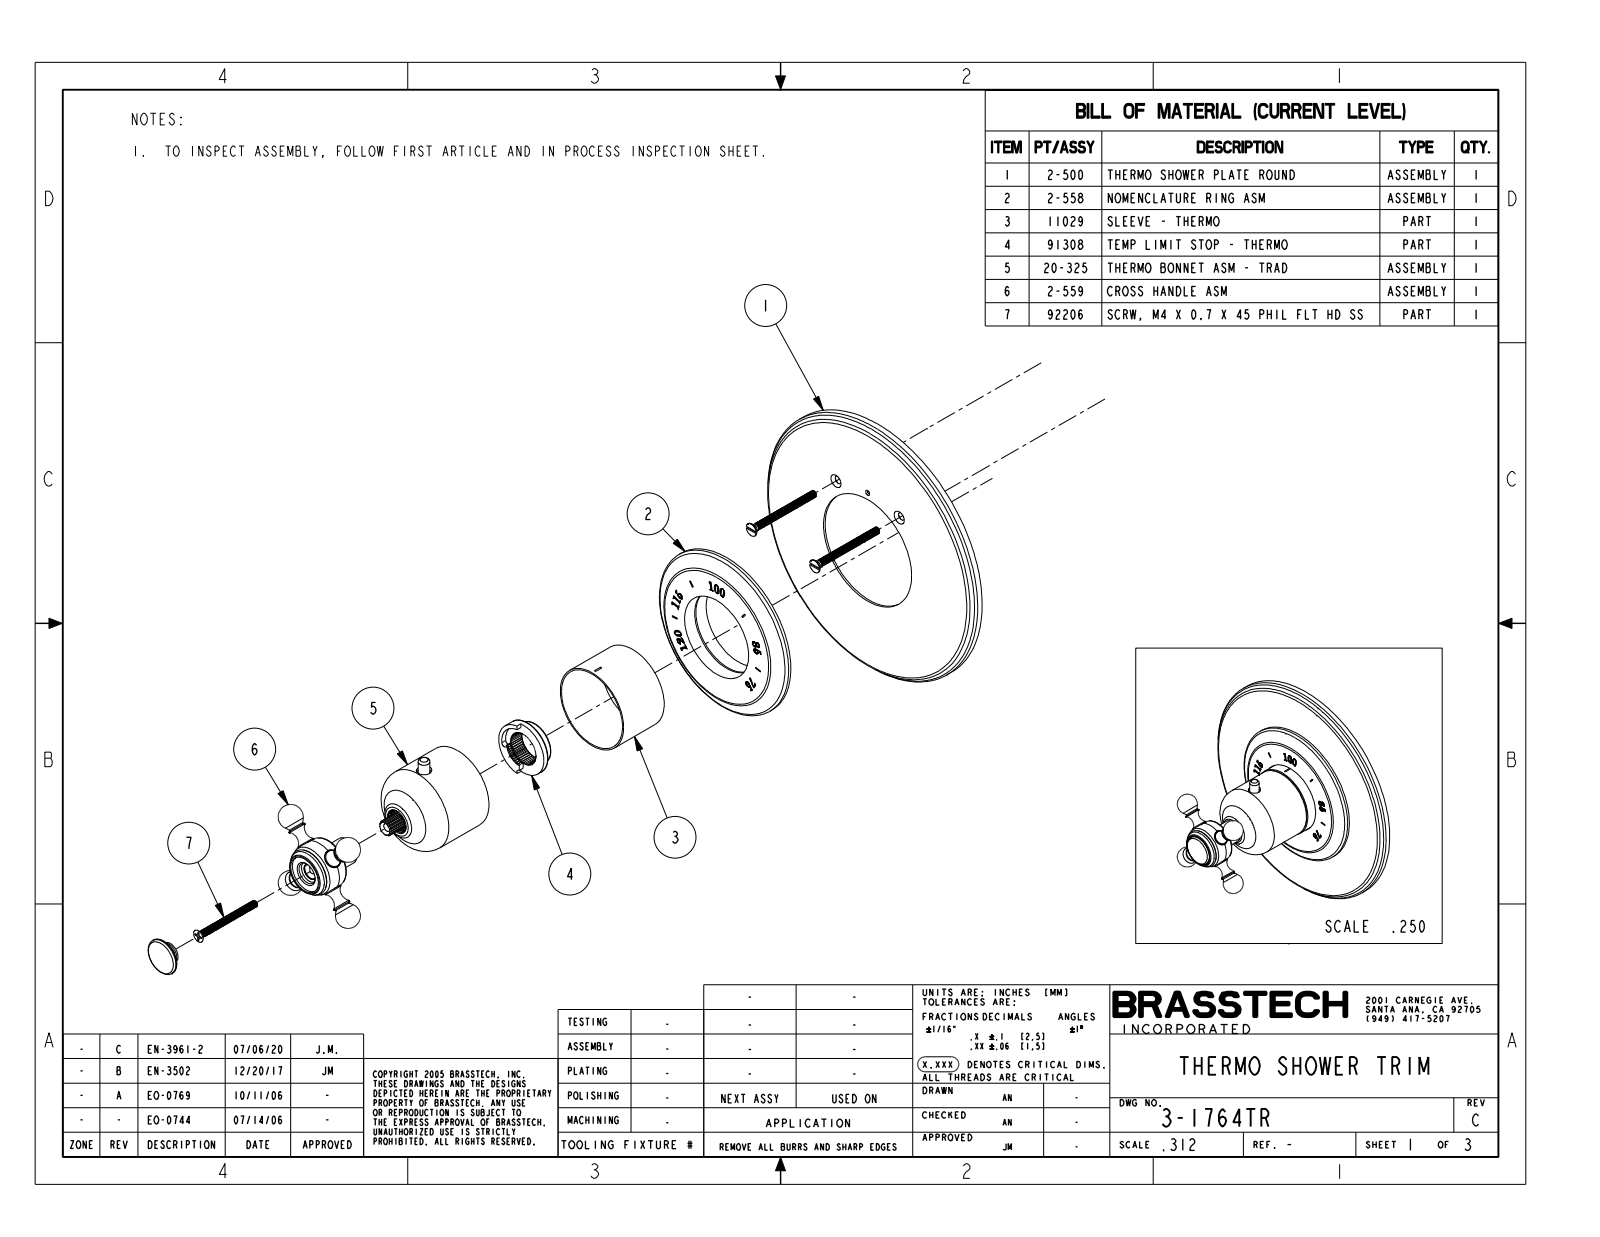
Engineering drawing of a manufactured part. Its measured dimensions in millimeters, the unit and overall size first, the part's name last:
Units: millimetres
Overall size (bounding box): 165.1 × 165.1 × 108
Round holes (diameter × count): ⌀10.4 ×1
Round bosses / shafts (diameter × count): ⌀165.1 ×1, ⌀101.3 ×1, ⌀50 ×1, ⌀49.3 ×1, ⌀15.9 ×1, ⌀10.2 ×1, ⌀10 ×1, ⌀6.6 ×1
Main face-to-face distances: 8, 15.9, 71.4, 63.4, 55.5, 85.9, 77.9, 70, 14.5, 71.9
Volume: 340 400 mm³ · Surface area: 61 010 mm²
Bodies: 1 solid, 126 faces (14 planar, 22 cylindrical, 90 other)
Part name (STEP PRODUCT): 3-1764TR
STEP written by: CREO PARAMETRIC BY PTC INC, 2018400 (CONFIG_CONTROL_DESIGN)
